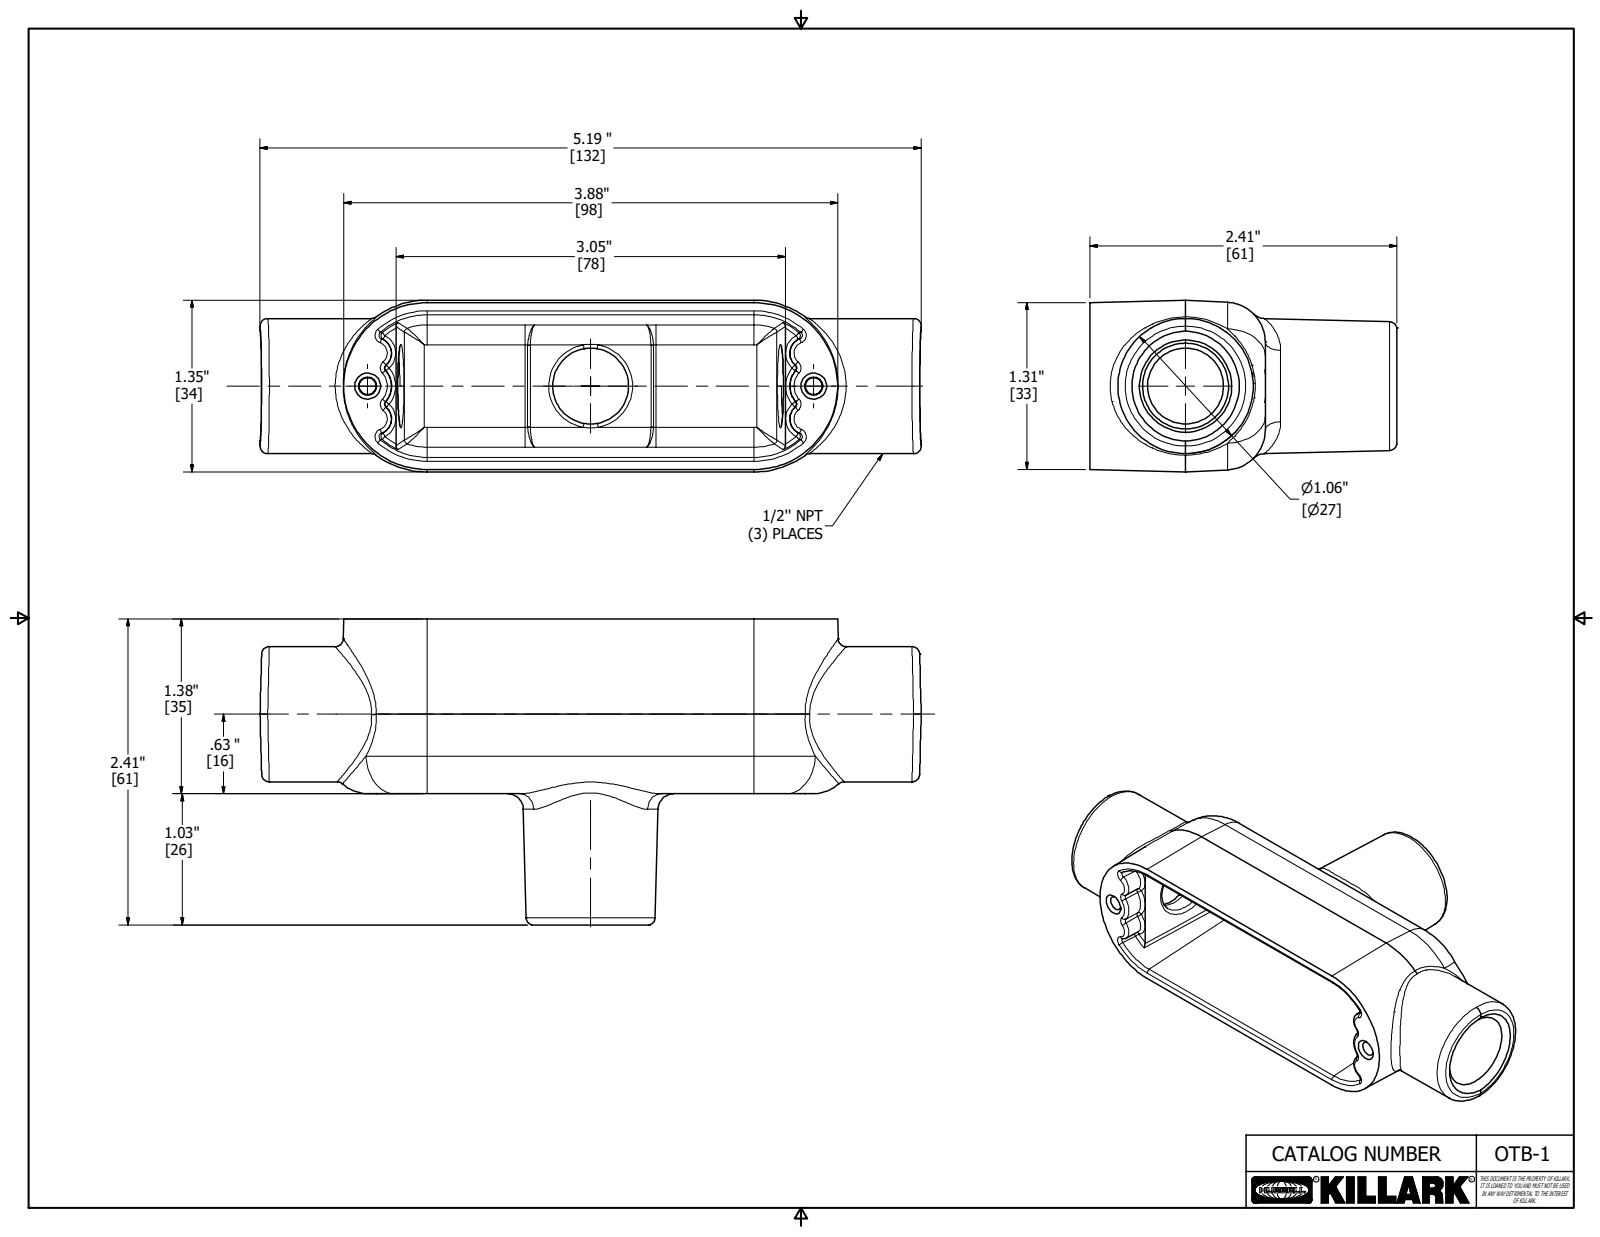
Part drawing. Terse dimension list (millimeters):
name: 13791-1
written by: Autodesk Inventor 2018 (AUTOMOTIVE_DESIGN)
unit: mm
bodies: 1 solid, 211 faces (60 planar, 21 cylindrical, 130 other)
size: 131.8 × 61.1 × 34.3
volume: 54 390 mm³; area: 27 750 mm²
holes: 2× ⌀15.1
bosses: 1× ⌀27
rounds: 6× R0.8, 6× R4, 2× R8
face distances: 2.4, 34.9, 32.5, 0.8, 1.6, 34.1, 2, 1.2, 0.4, 32.9
